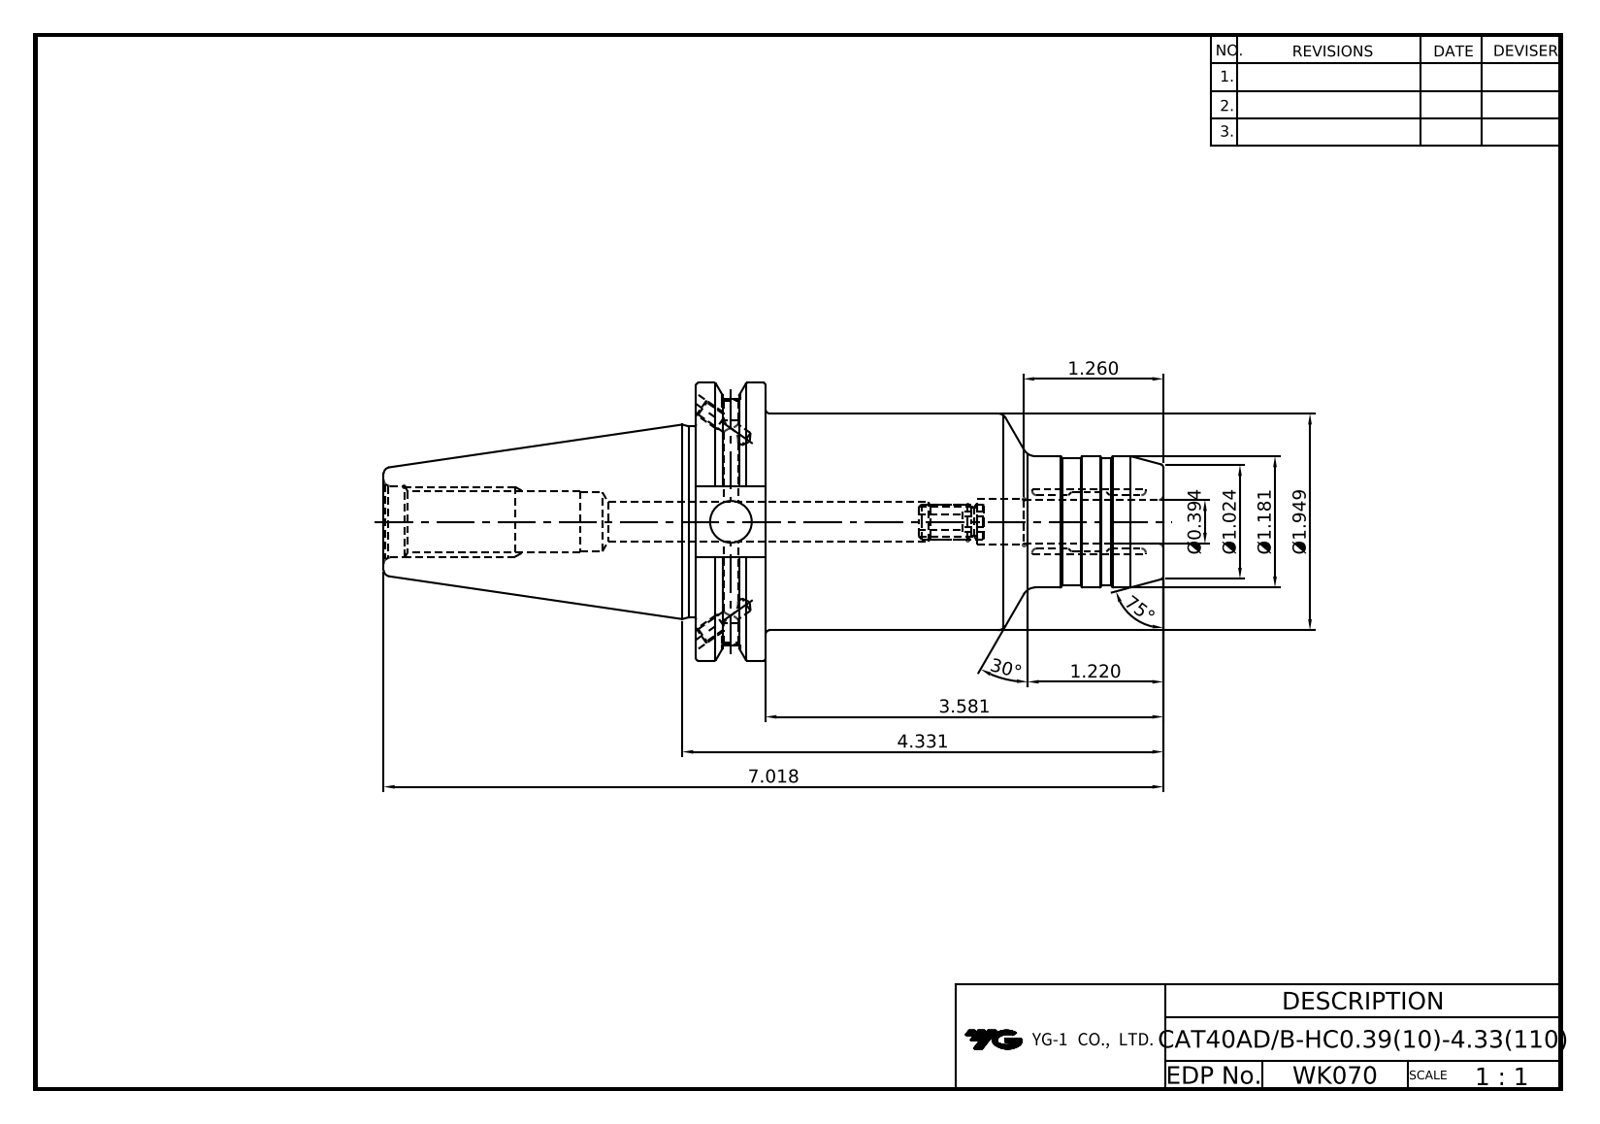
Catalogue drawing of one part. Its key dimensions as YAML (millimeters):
part_name: "LO-CAT40ADB-HC10-110"
step_written_by: "Autodesk Inventor 2020 (AUTOMOTIVE_DESIGN)"
units: millimeters
bodies: {solids: 1, faces: 108, planar: 34, cylindrical: 36, other: 38}
overall_size: [178.25, 63.5, 61.09]
volume: 229504
surface_area: 34397
round_holes:
  - {diameter: 3.24, count: 4}
  - {diameter: 4, count: 2}
  - {diameter: 4.2, count: 2}
  - {diameter: 6.92, count: 1}
  - {diameter: 9, count: 1}
  - {diameter: 9.53, count: 1}
  - {diameter: 10, count: 1}
  - {diameter: 10.6, count: 1}
  - {diameter: 13, count: 1}
  - {diameter: 13.39, count: 1}
  - {diameter: 16.3, count: 1}
round_bosses_or_shafts:
  - {diameter: 63.5, count: 1}
  - {diameter: 49.5, count: 1}
  - {diameter: 43.6, count: 1}
  - {diameter: 30, count: 1}
  - {diameter: 29, count: 1}
partial_cylinders:
  - {radius: 8.19, count: 1}
  - {radius: 28.15, count: 1}
face_to_face_distances: [15.88, 106.83, 90.95, 47.6, 16.38, 71.42, 87.3, 178.25, 77.47, 6.05]
